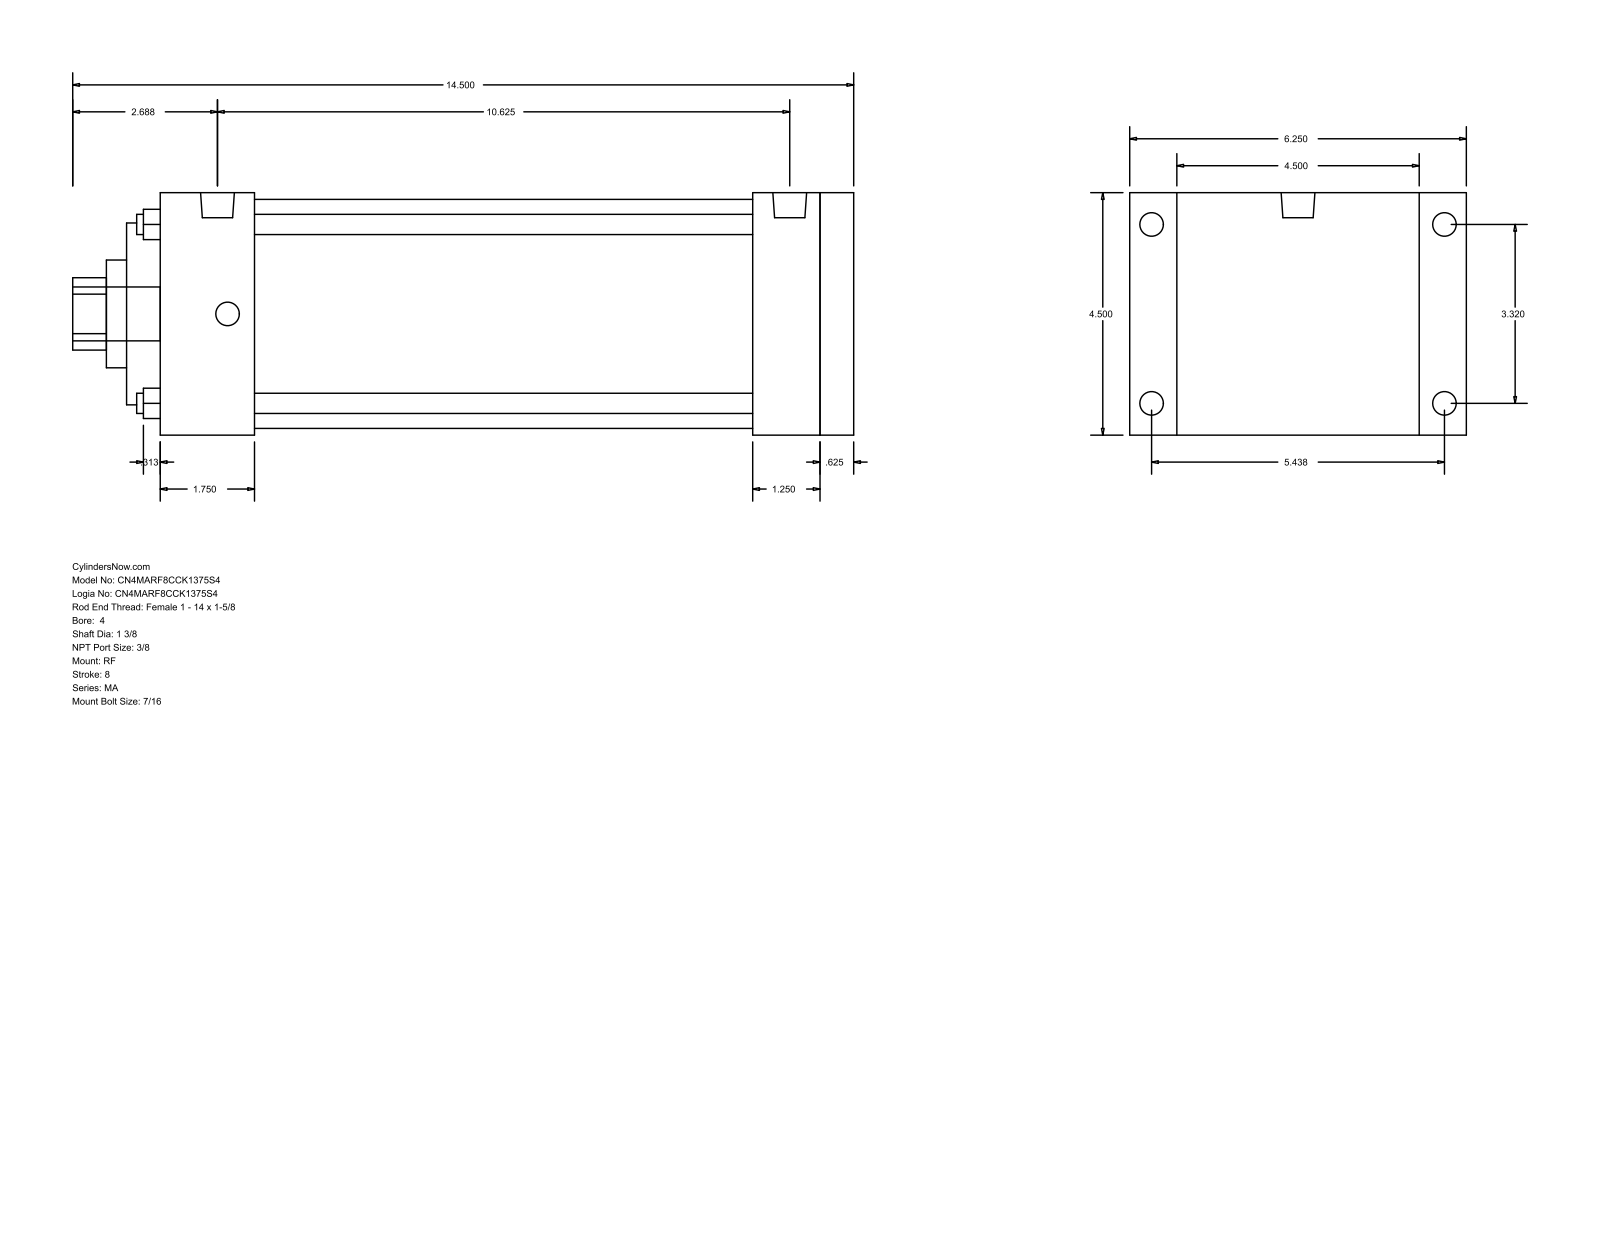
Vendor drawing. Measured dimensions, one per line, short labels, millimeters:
name: MA_RF__0400_1.375
written by: GSSL Pune (CONFIG_CONTROL_DESIGN)
unit: mm
bodies: 0 solids, 94 faces (65 planar, 29 cylindrical, 0 other)
size: 368.3 × 158.75 × 114.3
holes: 4× ⌀9.53, 1× ⌀34.92, 1× ⌀50.8, 1× ⌀85.72, 1× ⌀107.95
bosses: 8× ⌀11.11, 2× ⌀15.93, 1× ⌀25.4
rounds: 1× R17.06
face distances: 114.3, 327.03, 15.87, 311.16, 342.9, 22.23, 136.53, 295.28, 279.41, 31.75
hole spacings: 59.62, 84.32, 119.25
